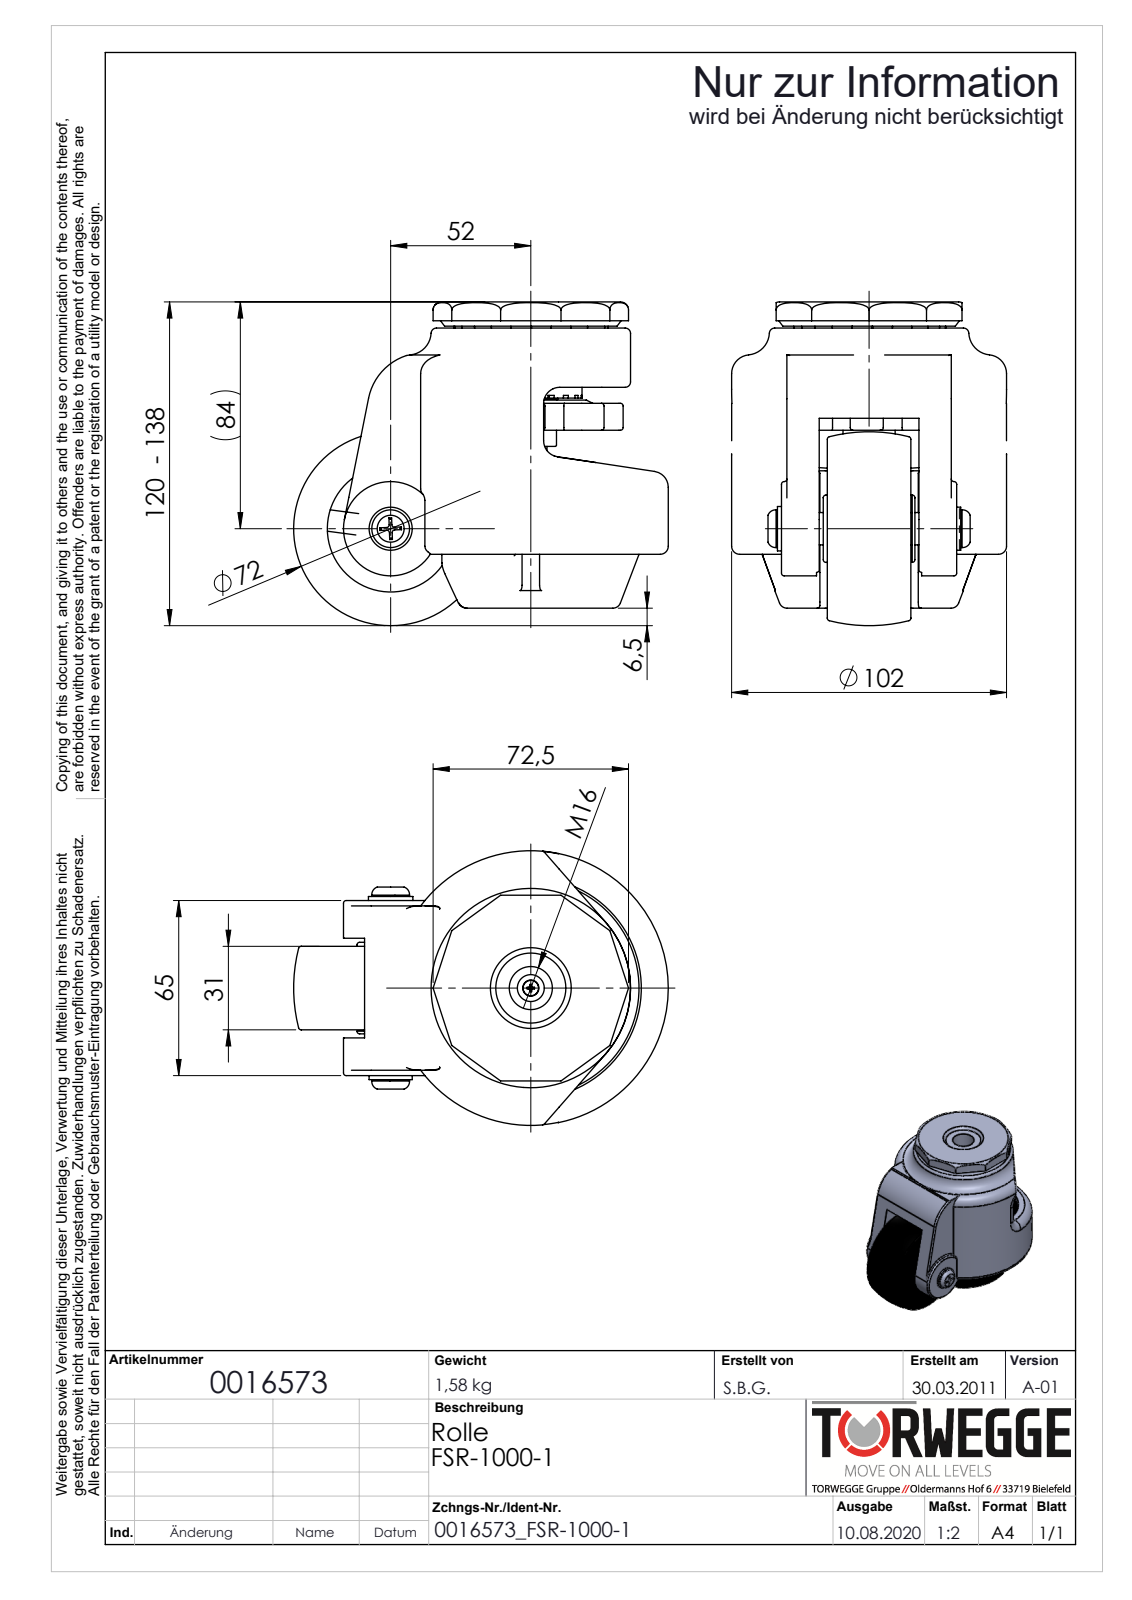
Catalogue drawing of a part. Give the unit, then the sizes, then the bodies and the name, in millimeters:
Units: millimetres
Overall size (bounding box): 139 × 120.2 × 102
Round holes (diameter × count): ⌀3 ×1, ⌀10 ×1, ⌀12.2 ×1, ⌀13 ×1, ⌀16 ×1, ⌀21 ×1, ⌀30 ×1, ⌀40 ×1, ⌀40.14 ×1, ⌀41.5 ×1, ⌀47 ×1, ⌀82 ×1
Round bosses / shafts (diameter × count): ⌀25 ×2, ⌀12 ×2, ⌀102 ×1, ⌀41.34 ×1, ⌀38 ×1, ⌀24.5 ×1, ⌀20 ×1, ⌀16.5 ×1
Partial cylindrical surfaces — rounded edges, fillets, slot ends (radius × count): R1 ×70, R0.5 ×30, R2 ×10, R8 ×8, R6 ×4, R4 ×1, R11.25 ×1, R14.5 ×1
Main face-to-face distances: 31, 51, 34, 3, 12, 62.7, 31.7, 15.06, 15.94, 47.64
Bodies: 0 solids, 832 faces (240 planar, 257 cylindrical, 335 other)
Part name (STEP PRODUCT): 0016573
STEP written by: SolidWorks 2018 (AUTOMOTIVE_DESIGN)
